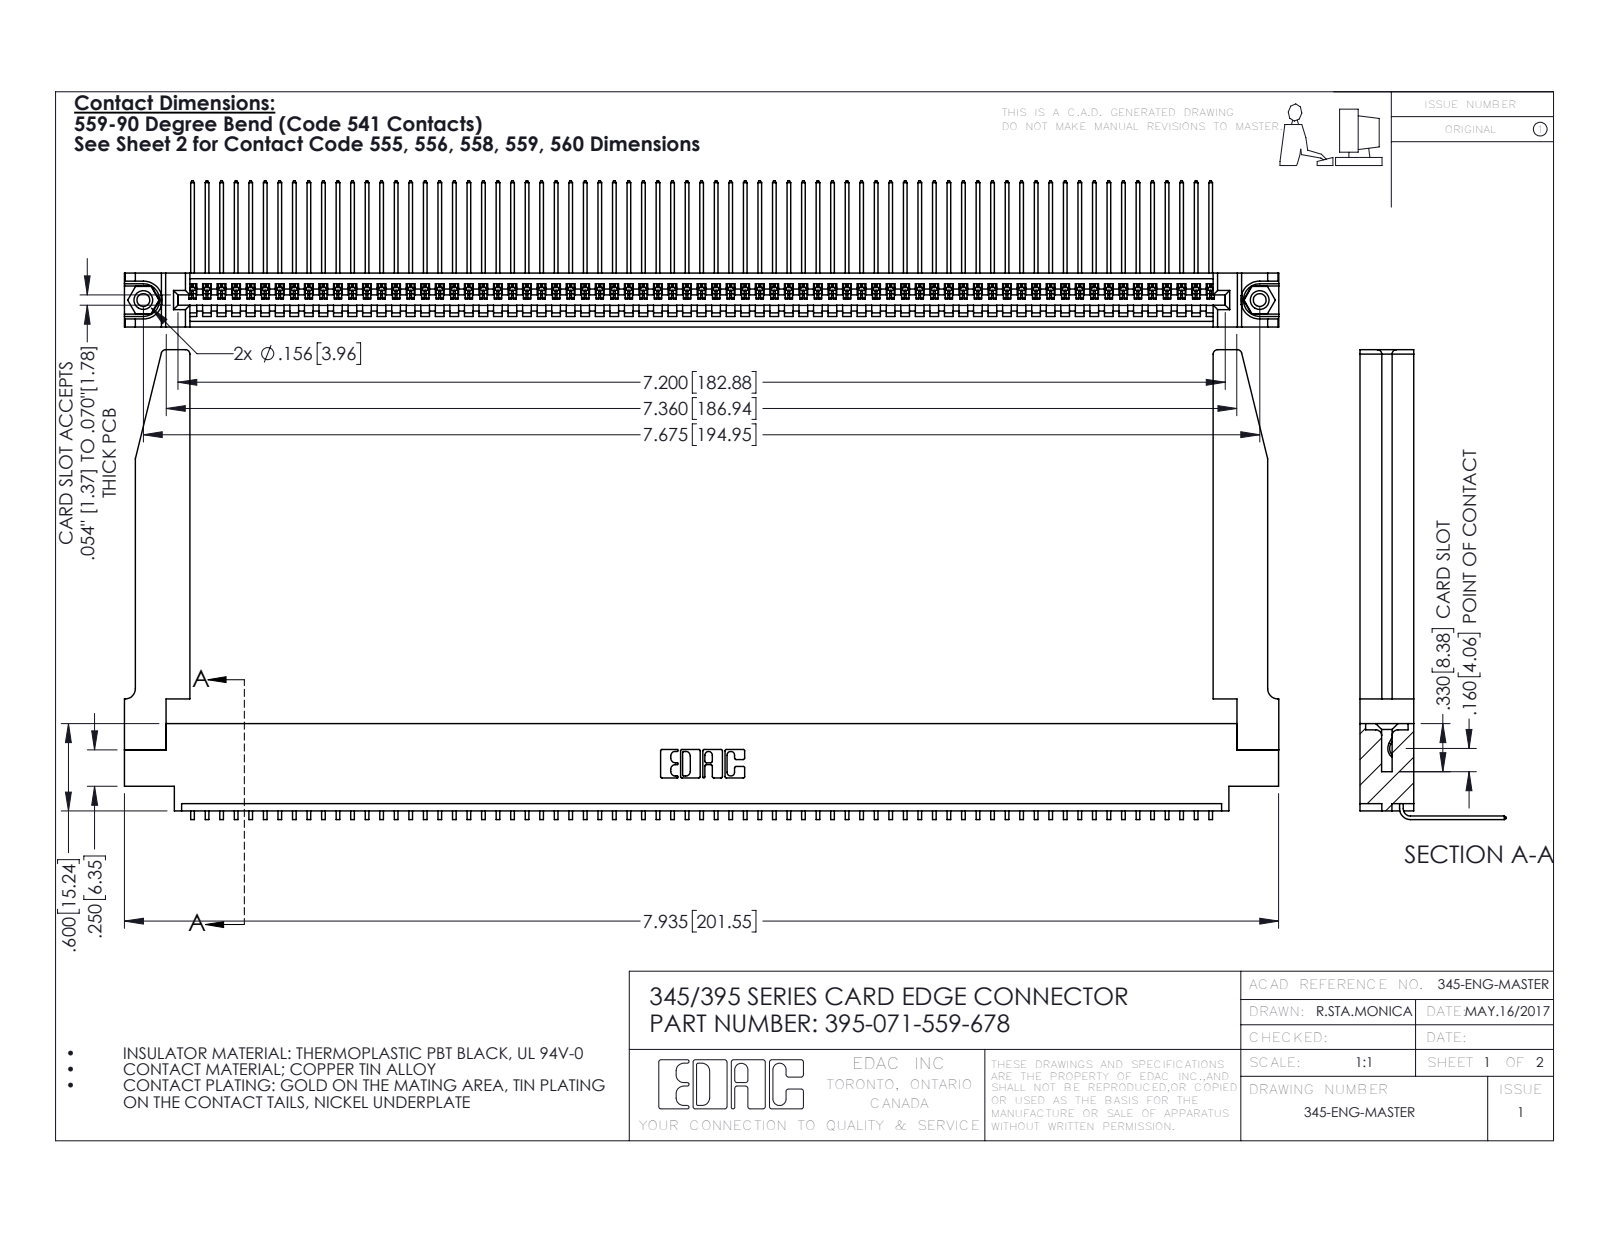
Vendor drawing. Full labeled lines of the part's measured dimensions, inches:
Part name (STEP PRODUCT): 345-250-001_345-250-001-102; 395-071-559-678; 345 Part_0.170 Offset - 0.156 Dia-TH; 345-292-001_558 559 Tail - 1 (+1 more)
STEP written by: SolidWorks 2016 (CONFIG_CONTROL_DESIGN)
Units: inches
Bodies: 76 solids, 4624 faces (3208 planar, 1364 cylindrical, 52 other)
Overall size (bounding box): 7.936 × 3.229 × 1.005
Volume: 1.665 in³ · Surface area: 53.75 in²
Round holes (diameter × count): ⌀0.089 ×2, ⌀0.125 ×2, ⌀0.156 ×2, ⌀0.064 ×1
Round bosses / shafts (diameter × count): ⌀0.155 ×2
Partial cylindrical surfaces — rounded edges, fillets, slot ends (radius × count): R0.006 ×142, R0.01 ×22, R0.03 ×8, R0.007 ×6, R0.031 ×6, R0.026 ×3, R0.031 ×2, R0.04 ×2
Main face-to-face distances: 0.37, 0.072, 0.298, 0.098, 0.272, 0.025, 0.2, 0.225, 0.175, 0.149
Hole centre spacings: 0.27, 7.439, 7.675
